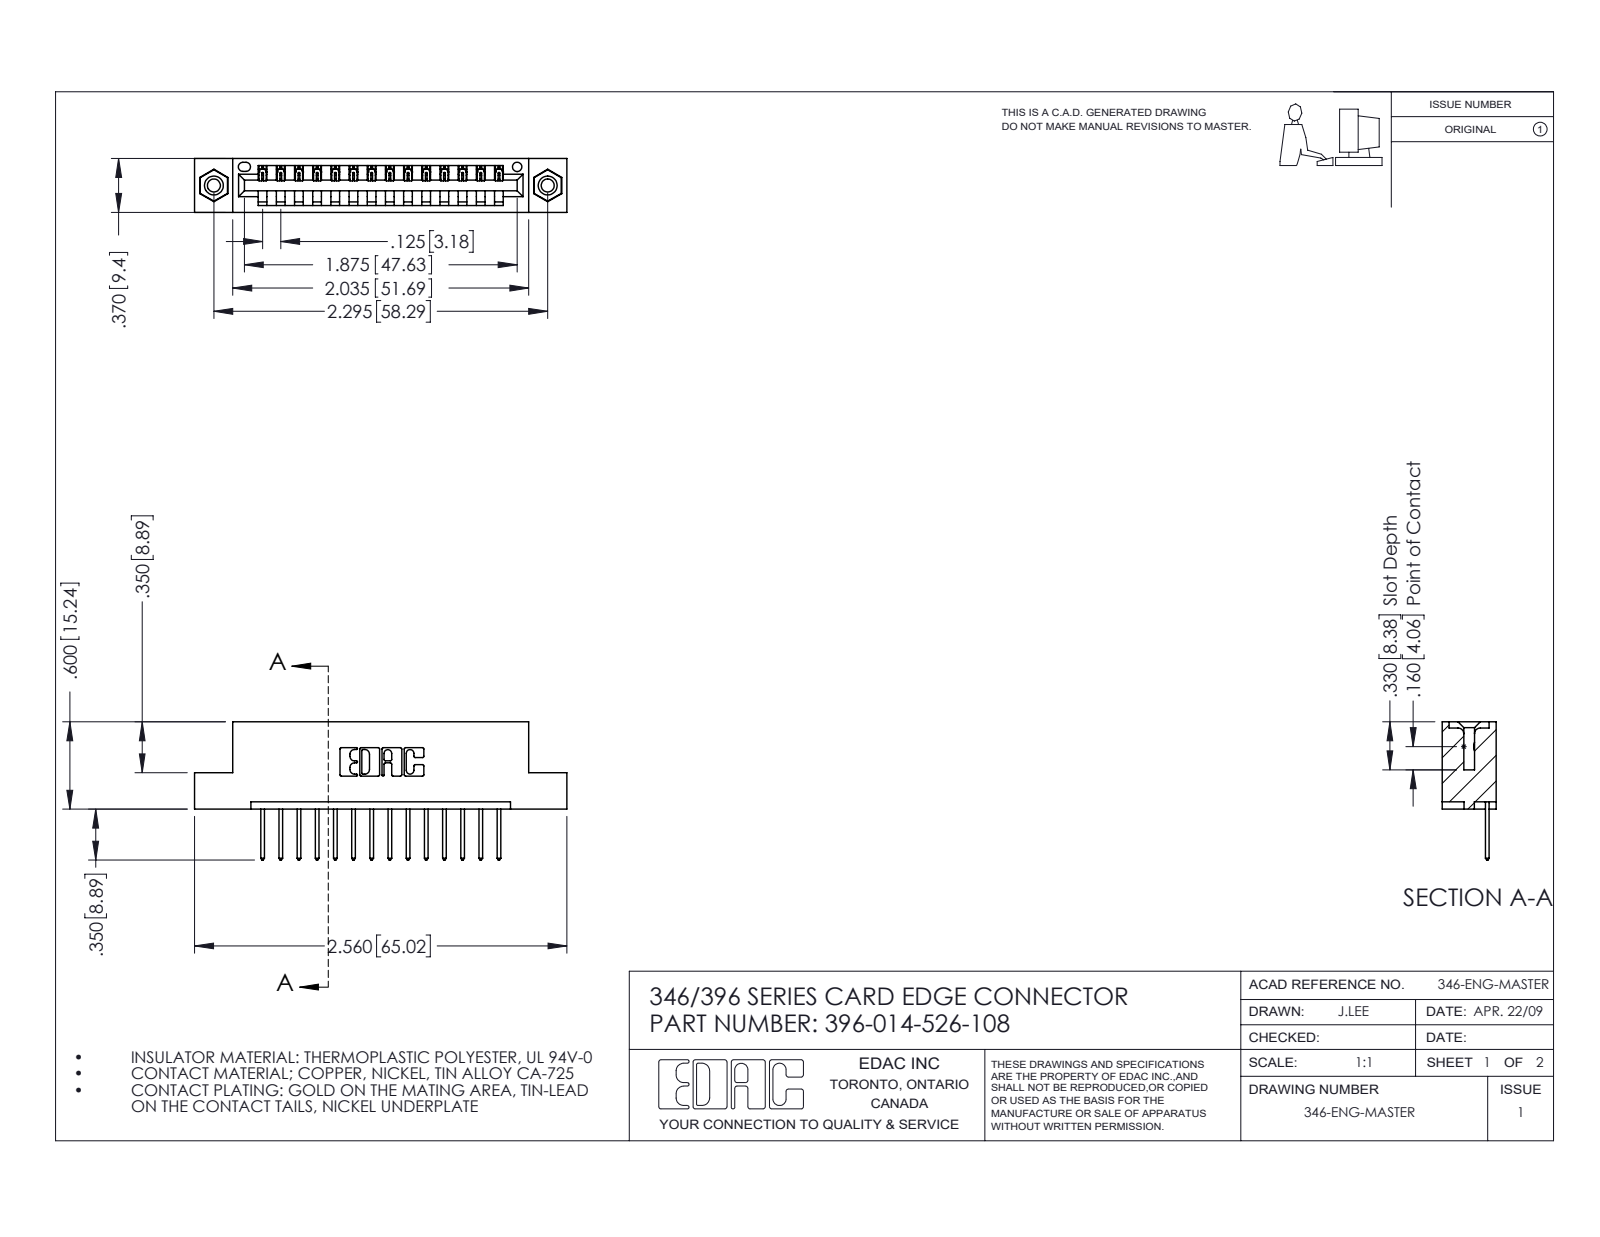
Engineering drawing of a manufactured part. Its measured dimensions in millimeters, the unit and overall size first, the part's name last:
Units: millimetres
Overall size (bounding box): 65 × 24.1 × 9.4
Round holes (diameter × count): ⌀2.3 ×2, ⌀3.2 ×2, ⌀4 ×2, ⌀1.6 ×1
Round bosses / shafts (diameter × count): ⌀3.9 ×2
Partial cylindrical surfaces — rounded edges, fillets, slot ends (radius × count): R0.2 ×28, R0.3 ×28, R0.3 ×22, R0.2 ×6, R0.8 ×6, R0.7 ×3, R0.8 ×2, R1 ×2
Main face-to-face distances: 6.4, 1.2, 8.2, 9.4, 1.8, 7.6, 0.6, 3.8, 5.6, 2.5
Hole centre spacings: 6.2, 53.1, 58.3
Volume: 6 010 mm³ · Surface area: 7 219 mm²
Bodies: 17 solids, 994 faces (668 planar, 310 cylindrical, 16 other)
Part name (STEP PRODUCT): 396-014-526-108; 345-292-001_345-293-126; 345-250-001_345-250-003-102; 346 Part_Flush Mounting Lugs - 0.156 Dia-TI
STEP written by: SolidWorks 2016 (CONFIG_CONTROL_DESIGN)
